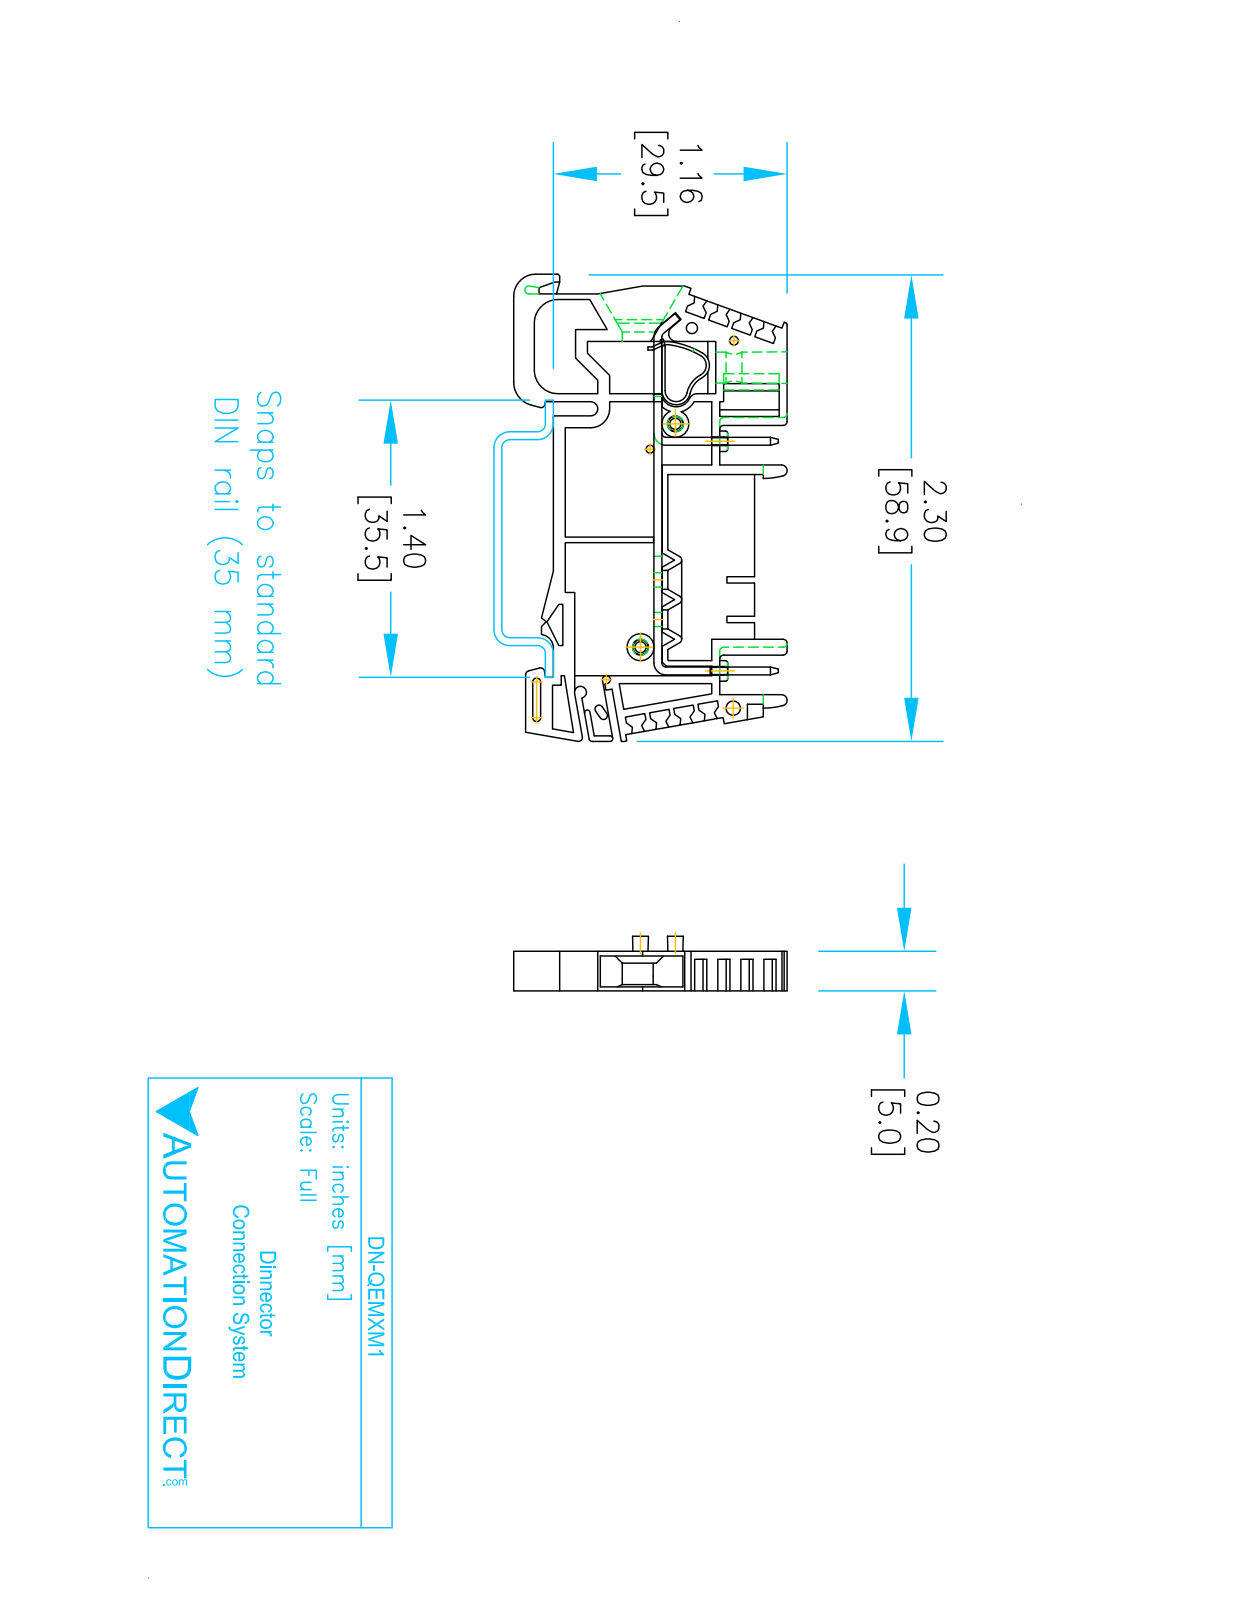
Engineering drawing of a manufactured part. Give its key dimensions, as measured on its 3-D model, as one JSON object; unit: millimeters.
{"part_name": "42560_DN-QEMXM1", "step_written_by": "SolidWorks 2013 (AUTOMOTIVE_DESIGN)", "units": "millimeters", "bodies": {"solids": 1, "faces": 298, "planar": 212, "cylindrical": 67, "other": 19}, "overall_size": [59, 34.5, 6.9], "volume_mm3": 6460, "surface_area_mm2": 5375, "round_holes": [[1.1, 1], [1.4, 1], [1.8, 1], [2, 1], [4.1, 1]], "round_bosses_or_shafts": [[2.6, 2]], "partial_cylinders_radius": [[0.2, 7], [0.5, 7], [0.3, 5], [3, 3], [0.7, 2], [10, 2], [0.35, 1], [0.75, 1]], "face_to_face_distances": [5, 1, 2, 3, 1.5, 24.9, 4, 0.8, 29, 6.2], "hole_center_spacings": [5.54, 12.26, 12.85, 36.63, 46.4, 48.26]}
